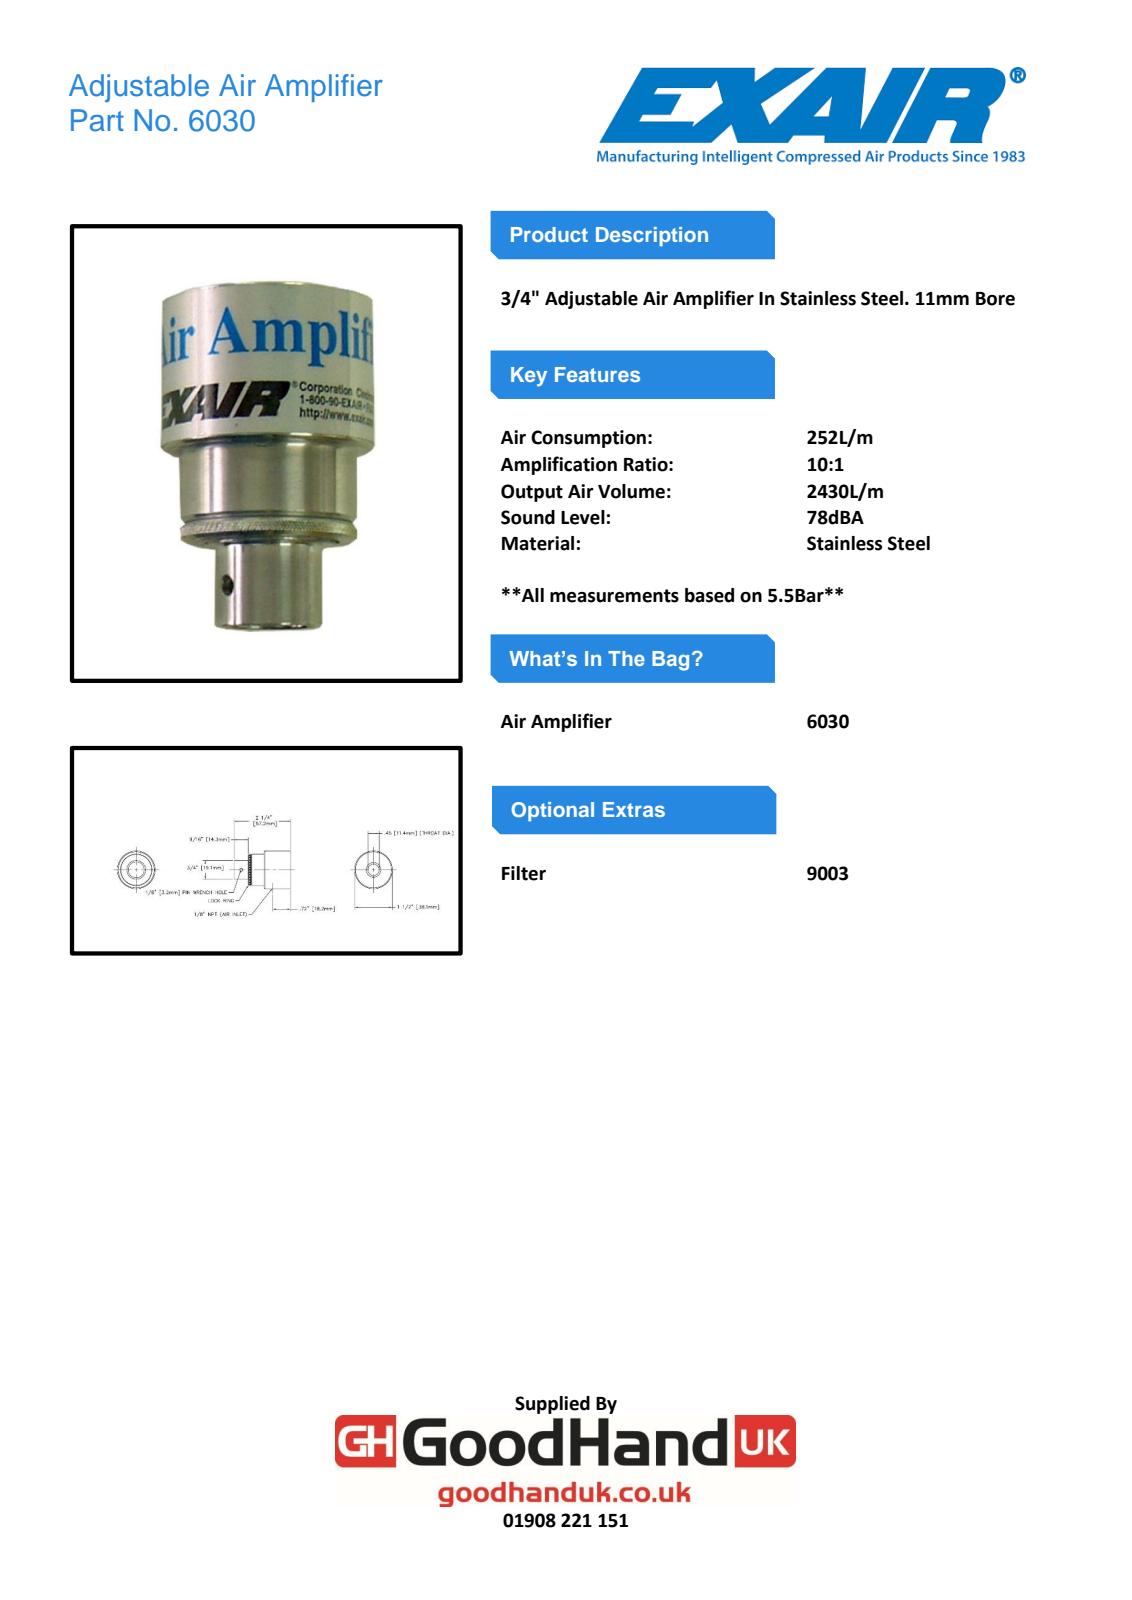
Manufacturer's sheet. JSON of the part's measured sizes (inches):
{"step_written_by": "Autodesk Inventor 2010 (AUTOMOTIVE_DESIGN)", "units": "inches", "bodies": {"solids": 3, "faces": 34, "planar": 10, "cylindrical": 10, "other": 14}, "overall_size": [2.219, 1.5, 1.5], "volume_in3": 2.042, "surface_area_in2": 23.89, "round_holes": [[0.125, 1], [0.875, 1], [0.938, 1]], "round_bosses_or_shafts": [[1.5, 1], [1.25, 1], [1.234, 1], [1, 1], [0.866, 1], [0.75, 1]], "face_to_face_distances": [1.093, 0.5, 0.593, 0.125, 0.625, 1.218, 0.094, 0.375, 0.532, 0.657]}
